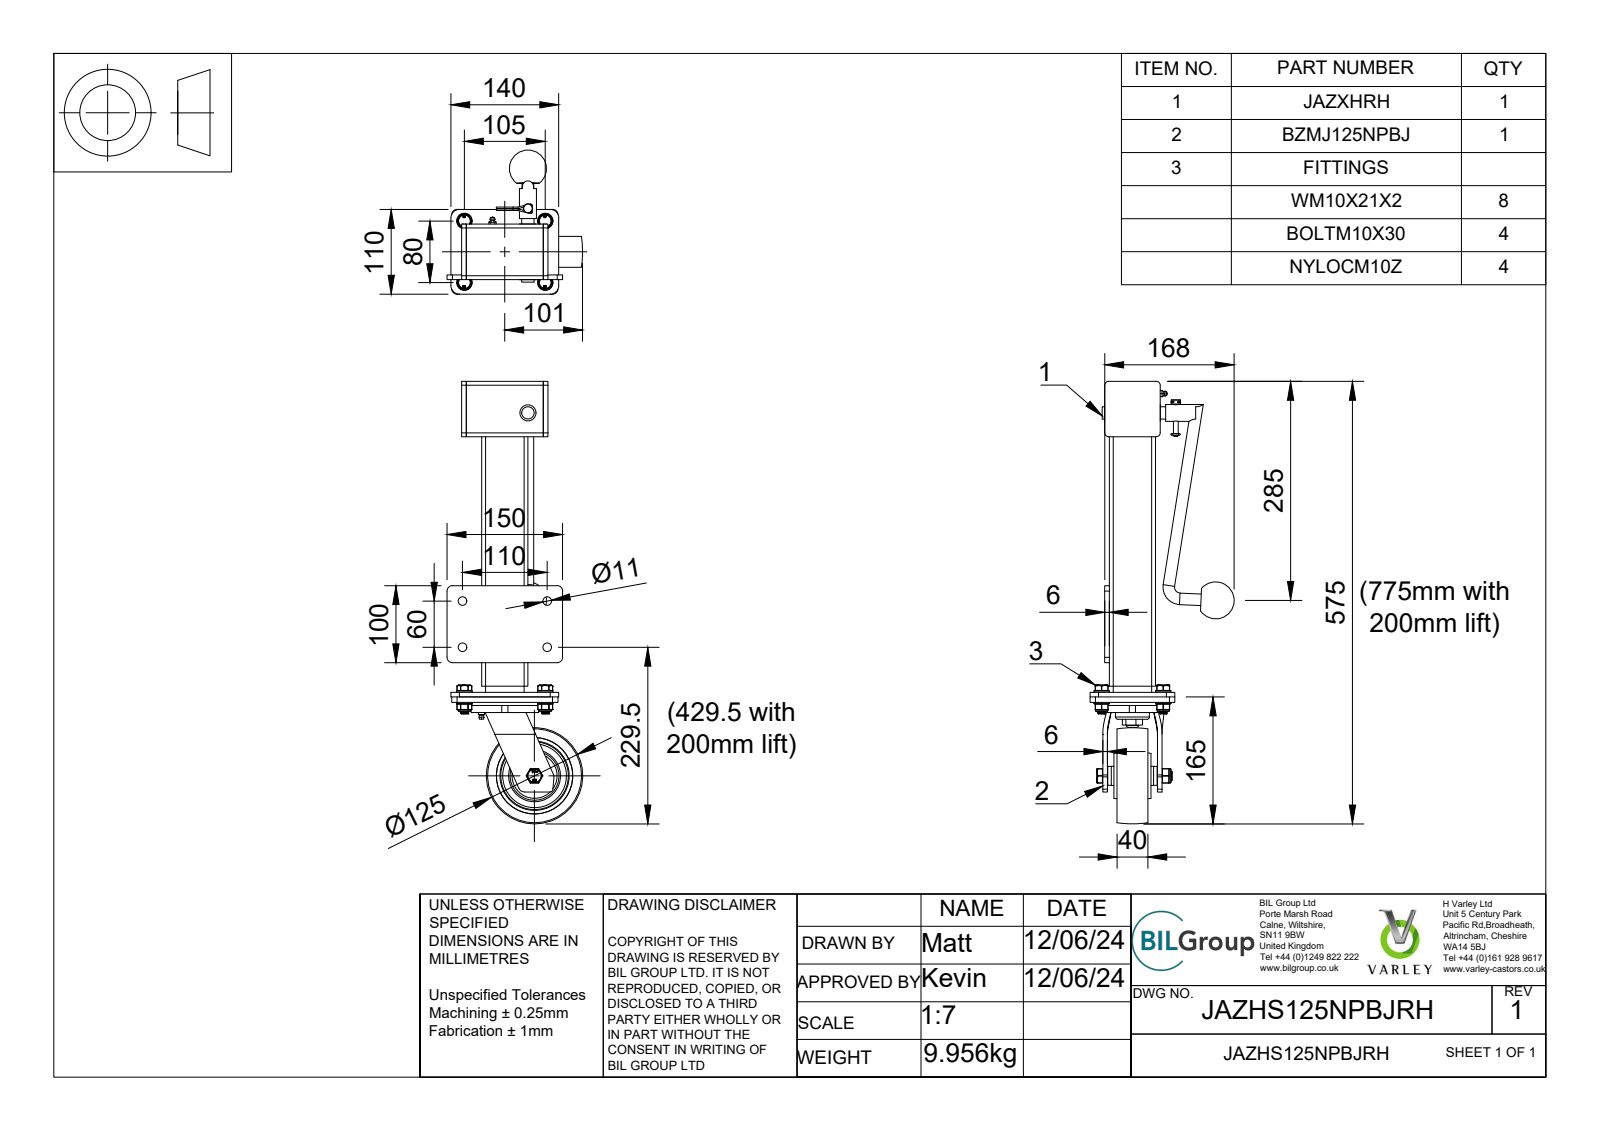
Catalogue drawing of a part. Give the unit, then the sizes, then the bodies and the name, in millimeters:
Units: millimetres
Overall size (bounding box): 575 × 187.03 × 176
Round holes (diameter × count): ⌀12 ×5, ⌀10 ×4, ⌀10.5 ×4, ⌀11 ×4, ⌀16 ×2, ⌀3 ×1, ⌀6.25 ×1, ⌀6.75 ×1, ⌀12.2 ×1, ⌀12.75 ×1, ⌀13 ×1, ⌀14 ×1
Round bosses / shafts (diameter × count): ⌀8 ×19, ⌀2 ×10, ⌀20 ×4, ⌀16 ×4, ⌀9.85 ×4, ⌀8.14 ×4, ⌀92 ×1, ⌀88 ×1
Partial cylindrical surfaces — rounded edges, fillets, slot ends (radius × count): R0.5 ×92, R0.33 ×16, R0.64 ×16, R5 ×9, R0.63 ×8, R0.64 ×8, R4.84 ×8, R5.33 ×8
Main face-to-face distances: 3.5, 6, 5, 1.5, 56.5, 51.5, 55, 62.5, 50, 68.5
Hole centre spacings: 66, 60, 80, 105, 110, 125.3, 132, 14
Volume: 2 207 000 mm³ · Surface area: 629 136 mm²
Bodies: 76 solids, 2218 faces (846 planar, 661 cylindrical, 711 other)
Part name (STEP PRODUCT): JAZHS125NPBJRH v3; JAZXHRH v1; JAZXHRH; BASE (+7 more)
STEP written by: Autodesk Translation Framework v13.14.0.145 (AUTOMOTIVE_DESIGN)
